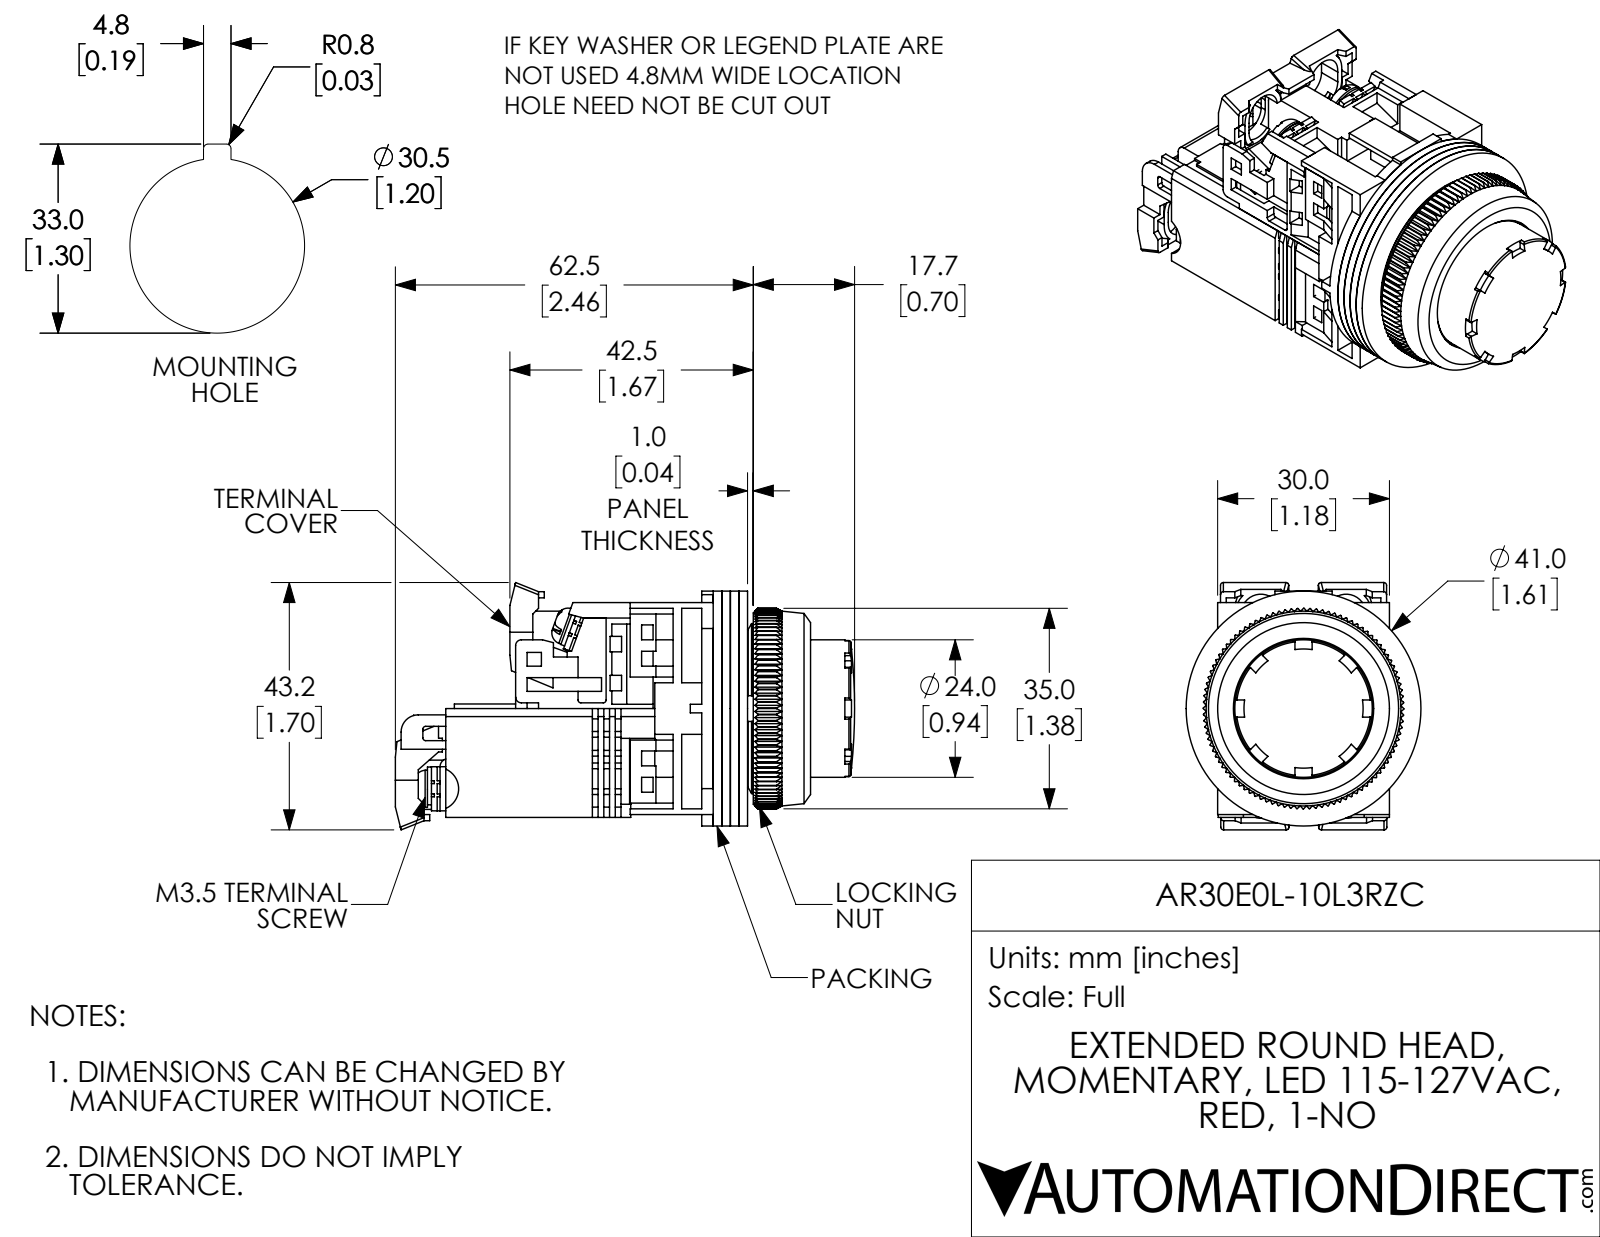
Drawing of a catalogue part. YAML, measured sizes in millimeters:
part_name: "AR30E0L-10L3RZC"
step_written_by: "SolidWorks 2017 (AUTOMOTIVE_DESIGN)"
units: millimeters
bodies: {solids: 27, faces: 1960, planar: 1368, cylindrical: 339, other: 253}
overall_size: [80.2, 43.2, 41]
volume: 47240
surface_area: 41310
round_holes:
  - {diameter: 3.5, count: 6}
  - {diameter: 3.6, count: 4}
  - {diameter: 3, count: 3}
  - {diameter: 12, count: 1}
  - {diameter: 18, count: 1}
  - {diameter: 18.5, count: 1}
  - {diameter: 20, count: 1}
  - {diameter: 24, count: 1}
  - {diameter: 24.5, count: 1}
  - {diameter: 28.5, count: 1}
  - {diameter: 31.8, count: 1}
round_bosses_or_shafts:
  - {diameter: 6.6, count: 4}
  - {diameter: 3.5, count: 2}
  - {diameter: 41, count: 1}
  - {diameter: 30, count: 1}
  - {diameter: 22, count: 1}
  - {diameter: 19.7, count: 1}
  - {diameter: 14, count: 1}
partial_cylinders:
  - {radius: 1.5, count: 17}
  - {radius: 0.3, count: 16}
  - {radius: 0.5, count: 13}
  - {radius: 3.5, count: 4}
  - {radius: 4.5, count: 4}
  - {radius: 1, count: 2}
  - {radius: 3, count: 2}
  - {radius: 0.4, count: 1}
face_to_face_distances: [1.5, 3, 4.5, 19, 1, 0.5, 2, 36, 17.5, 1.2]
hole_center_spacings: [14.7, 0.5, 7.5, 7.6, 7.6, 14.8, 14.8, 15.4]
